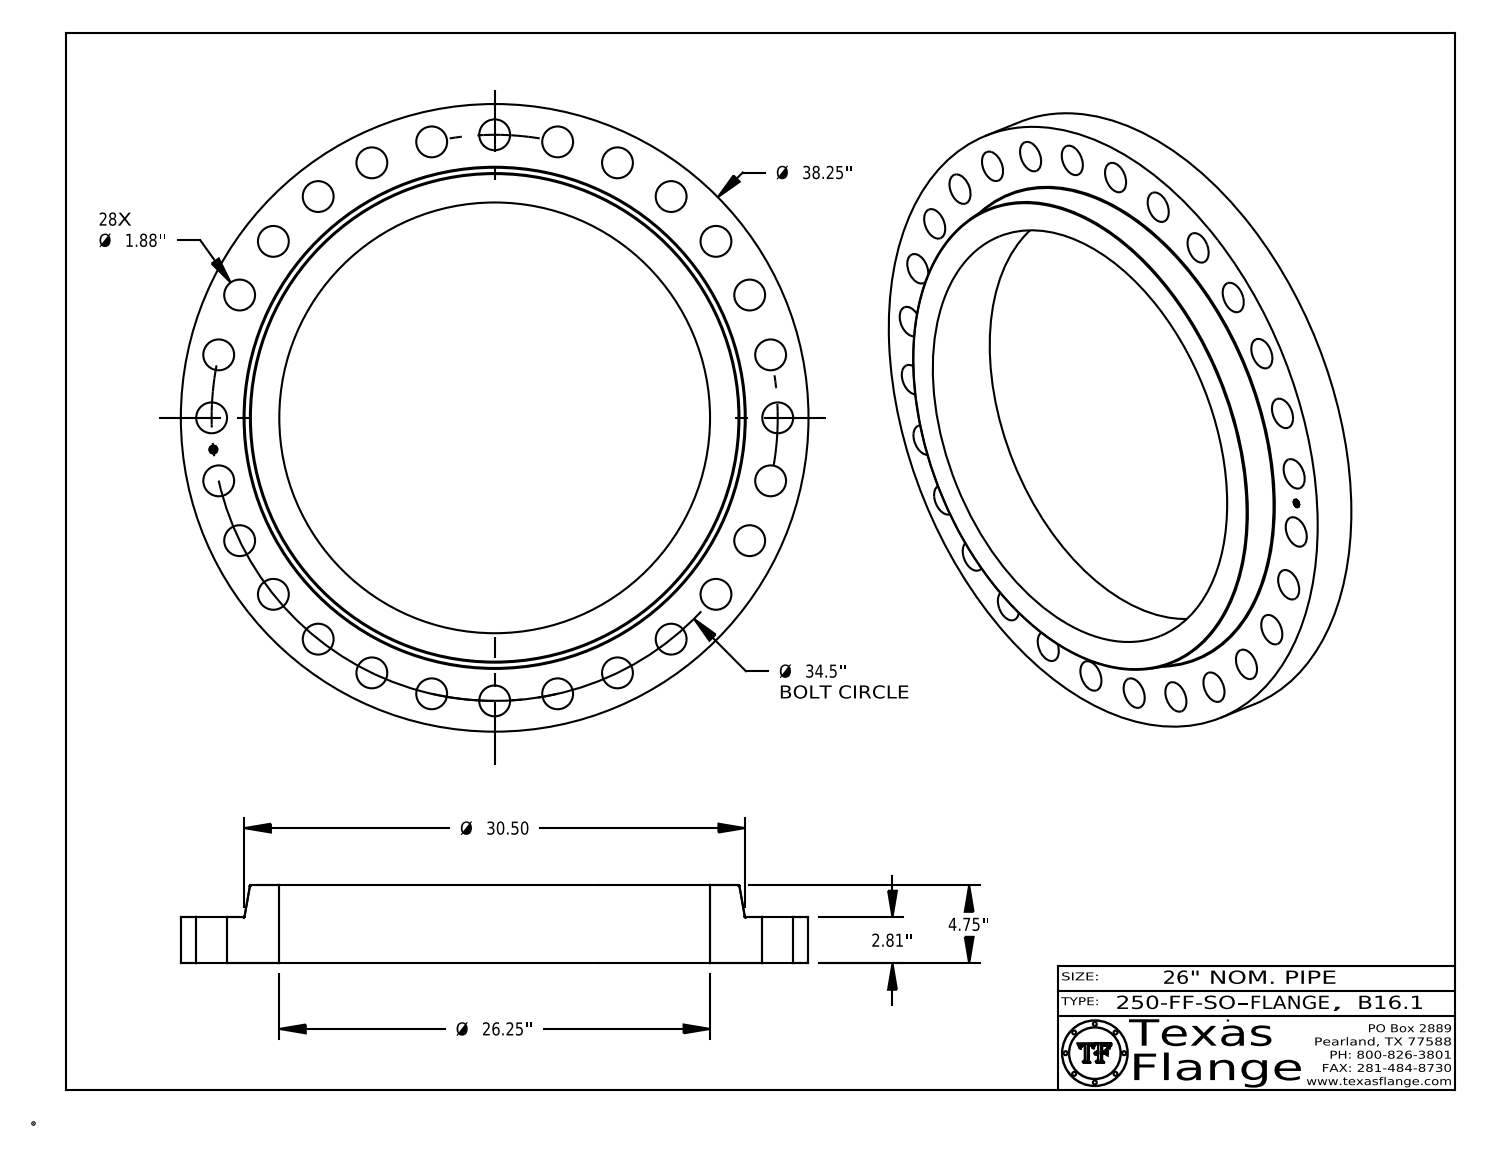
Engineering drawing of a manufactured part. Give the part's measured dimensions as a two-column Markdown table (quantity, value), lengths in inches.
| quantity | value |
| --- | --- |
| part name | B16.1, Class 250-FF-SO |
| STEP written by | CATIA V5 STEP AP214 (AUTOMOTIVE_DESIGN) |
| units | inches |
| bodies | 1 solid, 454 faces (368 planar, 80 cylindrical, 6 other) |
| overall size | 38.25 × 38.25 × 4.75 |
| volume | 1 826 in³ |
| surface area | 2 406 in² |
| round holes (diameter × count) | 1.88 × 28, 0.495 × 1, 26.25 × 1 |
| round bosses / shafts (diameter × count) | 0.03 × 8, 38.25 × 1, 0.39 × 1 |
| main face-to-face distances | 2.81, 4.75, 1.94, 2.795, 0.015, 1.955, 0.148, 0.144, 0.027, 0.096 |
| hole center spacings | 17.25, 26.973, 34.283, 14.969, 18.355, 32.564, 33.635, 11.394 |
